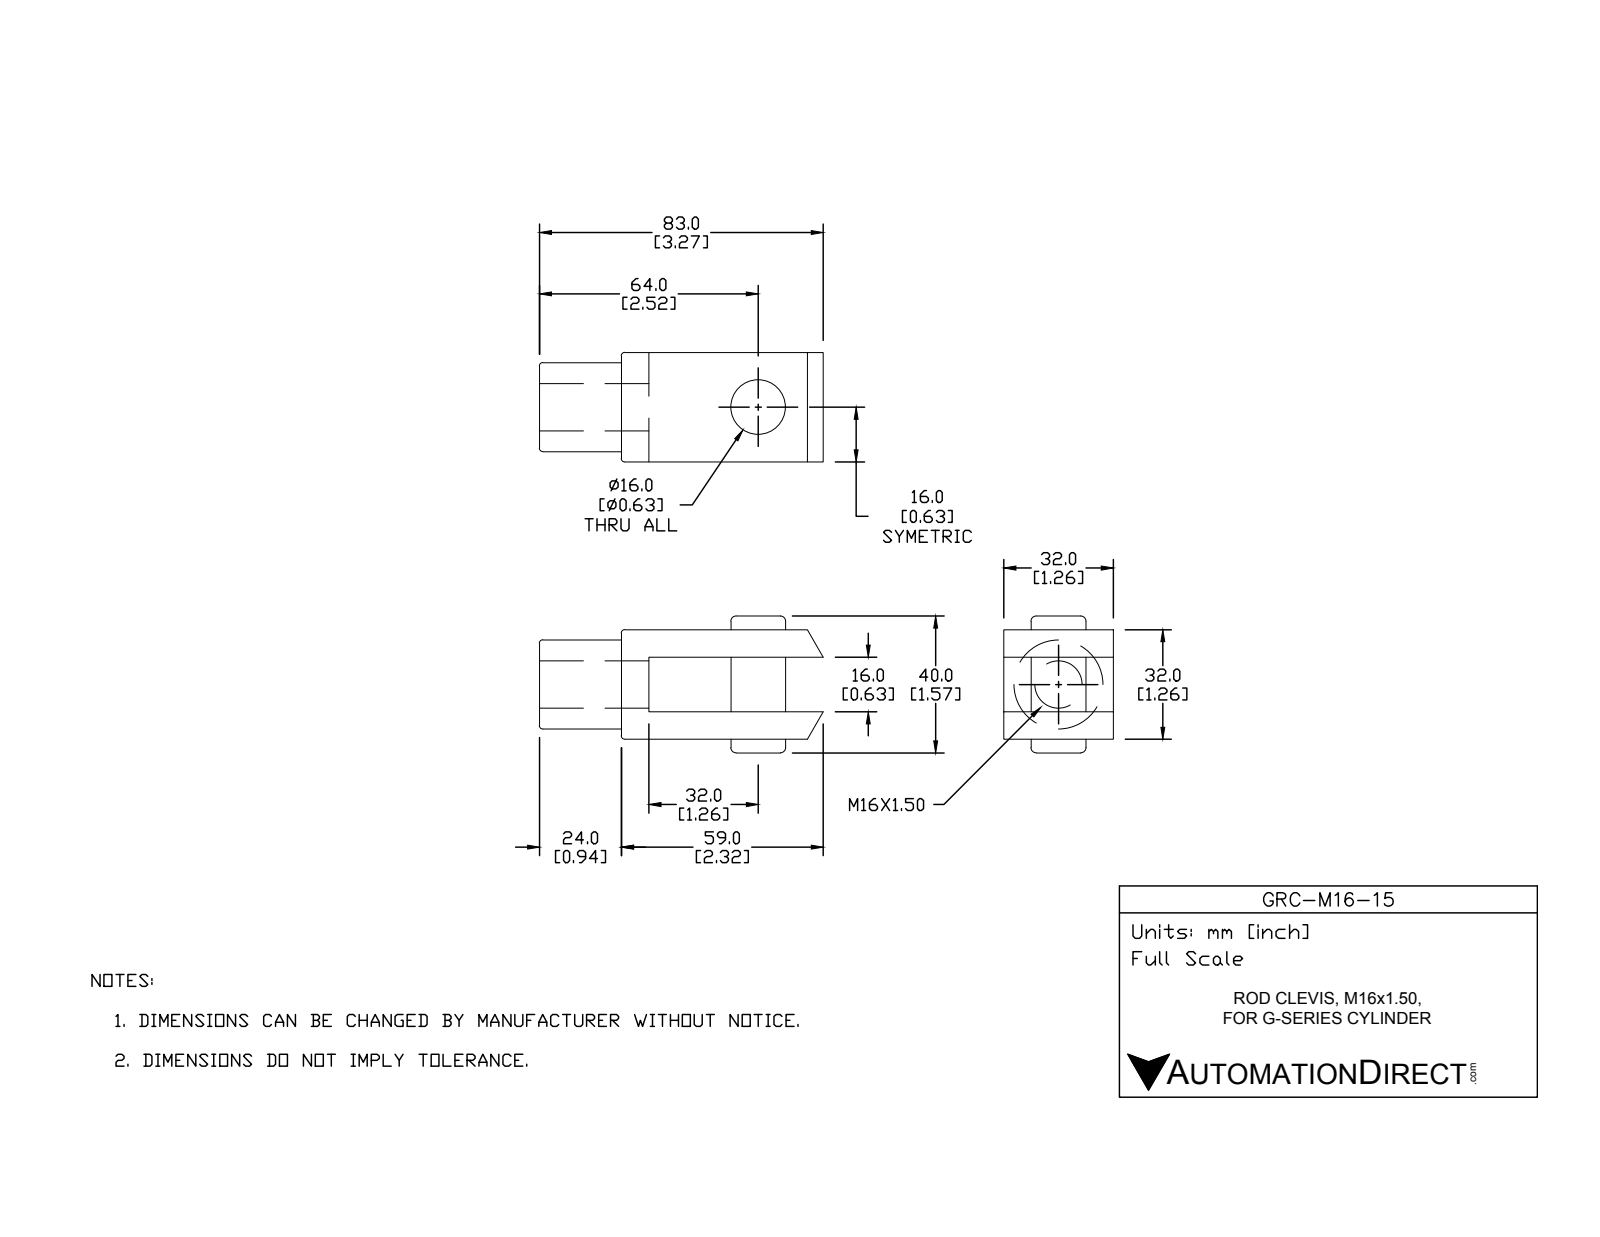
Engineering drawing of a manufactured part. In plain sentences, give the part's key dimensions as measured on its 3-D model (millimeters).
The part is named "GRC-M16-15". Its 3-D file was written by "SolidWorks 2017 (AUTOMOTIVE_DESIGN)". It is 1 solid with 33 faces: 13 planar, 14 cylindrical and 6 other. Overall it measures 83 by 40 by 32 millimeters. Its volume is 44 483 cubic millimeters and its surface area 14 575 square millimeters. Round holes: 1 of diameter 14.5. Round bosses or shafts: 1 of diameter 26, 1 of diameter 16. Partial cylindrical surfaces (rounded edges, fillets, slot ends): 4 of radius 1. The main face-to-face distances are 8, 24, 32, 16, 4, 12, 28, 36, 40.
